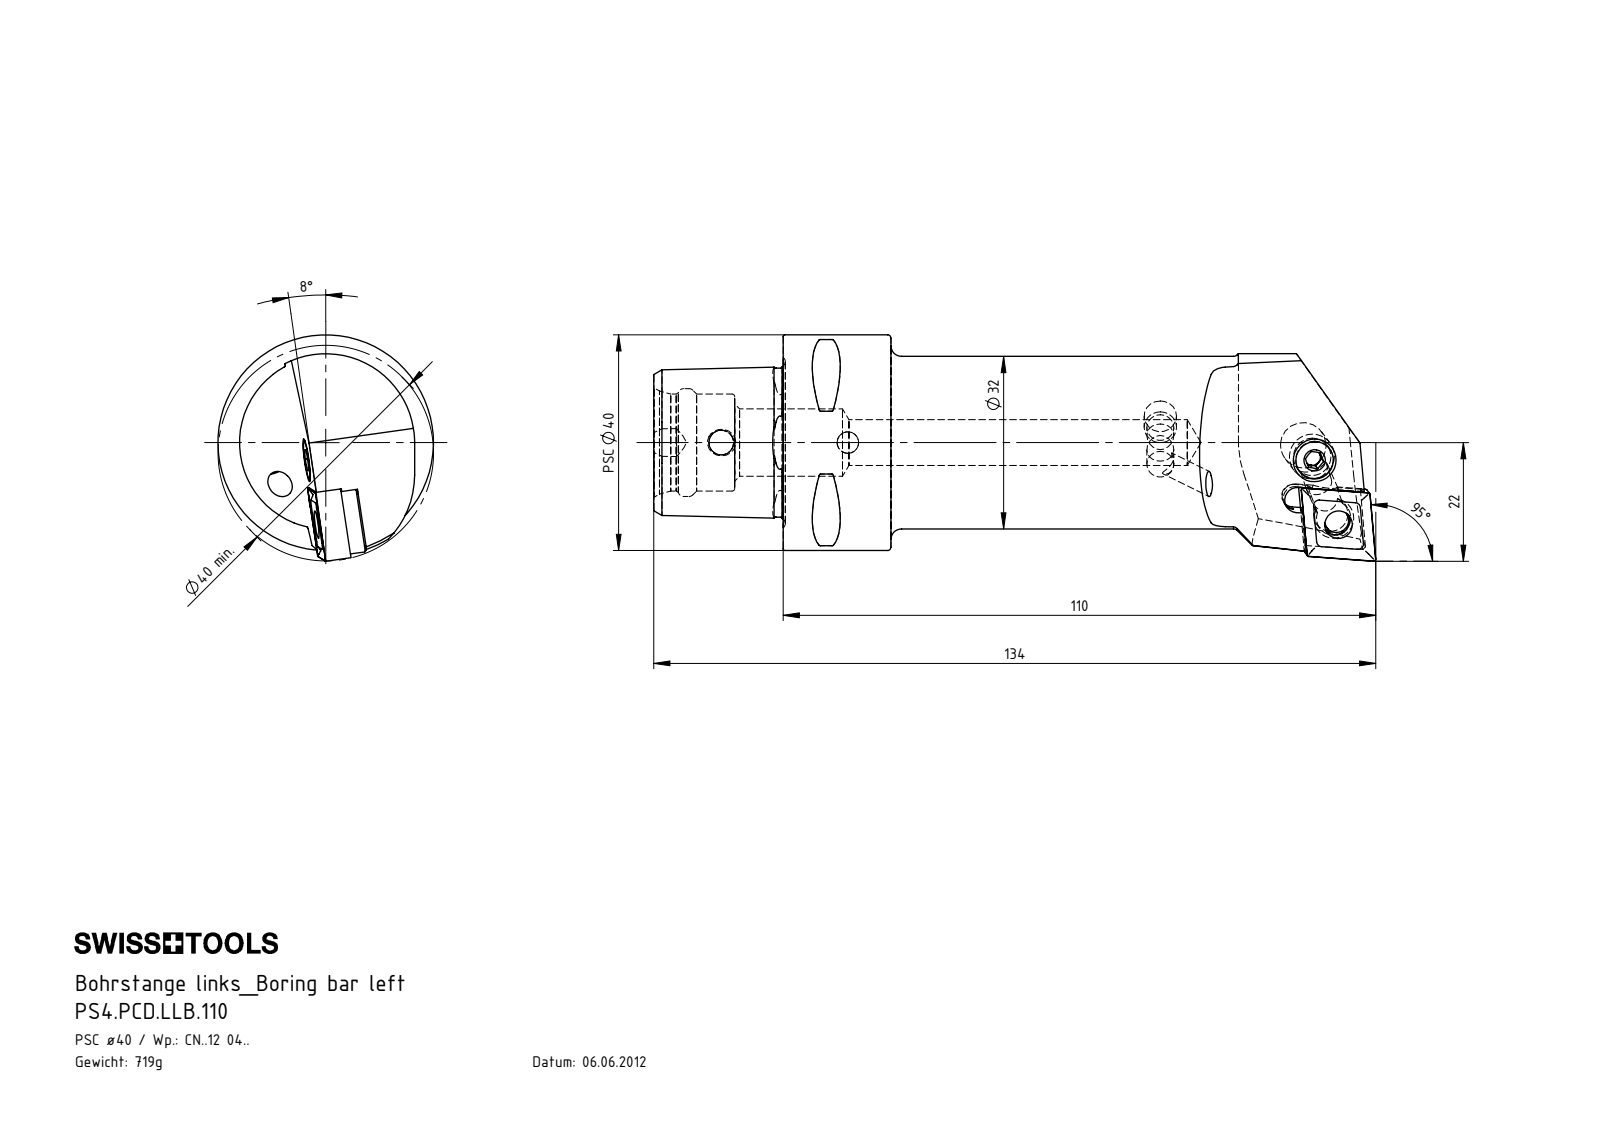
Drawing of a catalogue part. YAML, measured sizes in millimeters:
part_name: "PS4-PCD.LLB.110_A; WCD-ER2.101.003_A; CNMG120404; WCD-ER3.101.000_A (+4 more)"
step_written_by: "SolidWorks 2017 (AUTOMOTIVE_DESIGN)"
units: millimeters
bodies: {solids: 8, faces: 367, planar: 94, cylindrical: 90, other: 183}
overall_size: [134, 42, 40]
volume: 90725
surface_area: 22285
round_holes:
  - {diameter: 4, count: 1}
  - {diameter: 4.2, count: 1}
  - {diameter: 4.6, count: 1}
  - {diameter: 5, count: 1}
  - {diameter: 5.16, count: 1}
  - {diameter: 6.4, count: 1}
  - {diameter: 7, count: 1}
  - {diameter: 8.4, count: 1}
  - {diameter: 8.5, count: 1}
  - {diameter: 12.5, count: 1}
  - {diameter: 18, count: 1}
  - {diameter: 20, count: 1}
round_bosses_or_shafts:
  - {diameter: 40, count: 1}
  - {diameter: 32, count: 1}
  - {diameter: 8, count: 1}
  - {diameter: 7.9, count: 1}
  - {diameter: 6.4, count: 1}
  - {diameter: 6, count: 1}
  - {diameter: 4.5, count: 1}
  - {diameter: 3.55, count: 1}
partial_cylinders:
  - {radius: 0.3, count: 8}
  - {radius: 0.4, count: 4}
  - {radius: 1, count: 4}
  - {radius: 2.5, count: 2}
  - {radius: 3, count: 2}
  - {radius: 2.1, count: 1}
  - {radius: 2.2, count: 1}
  - {radius: 2.35, count: 1}
face_to_face_distances: [4.49, 20, 24, 44, 3.18, 7.67, 15.52, 0.5, 4.71, 11.7]
hole_center_spacings: [12.8, 12.86, 23.5]
